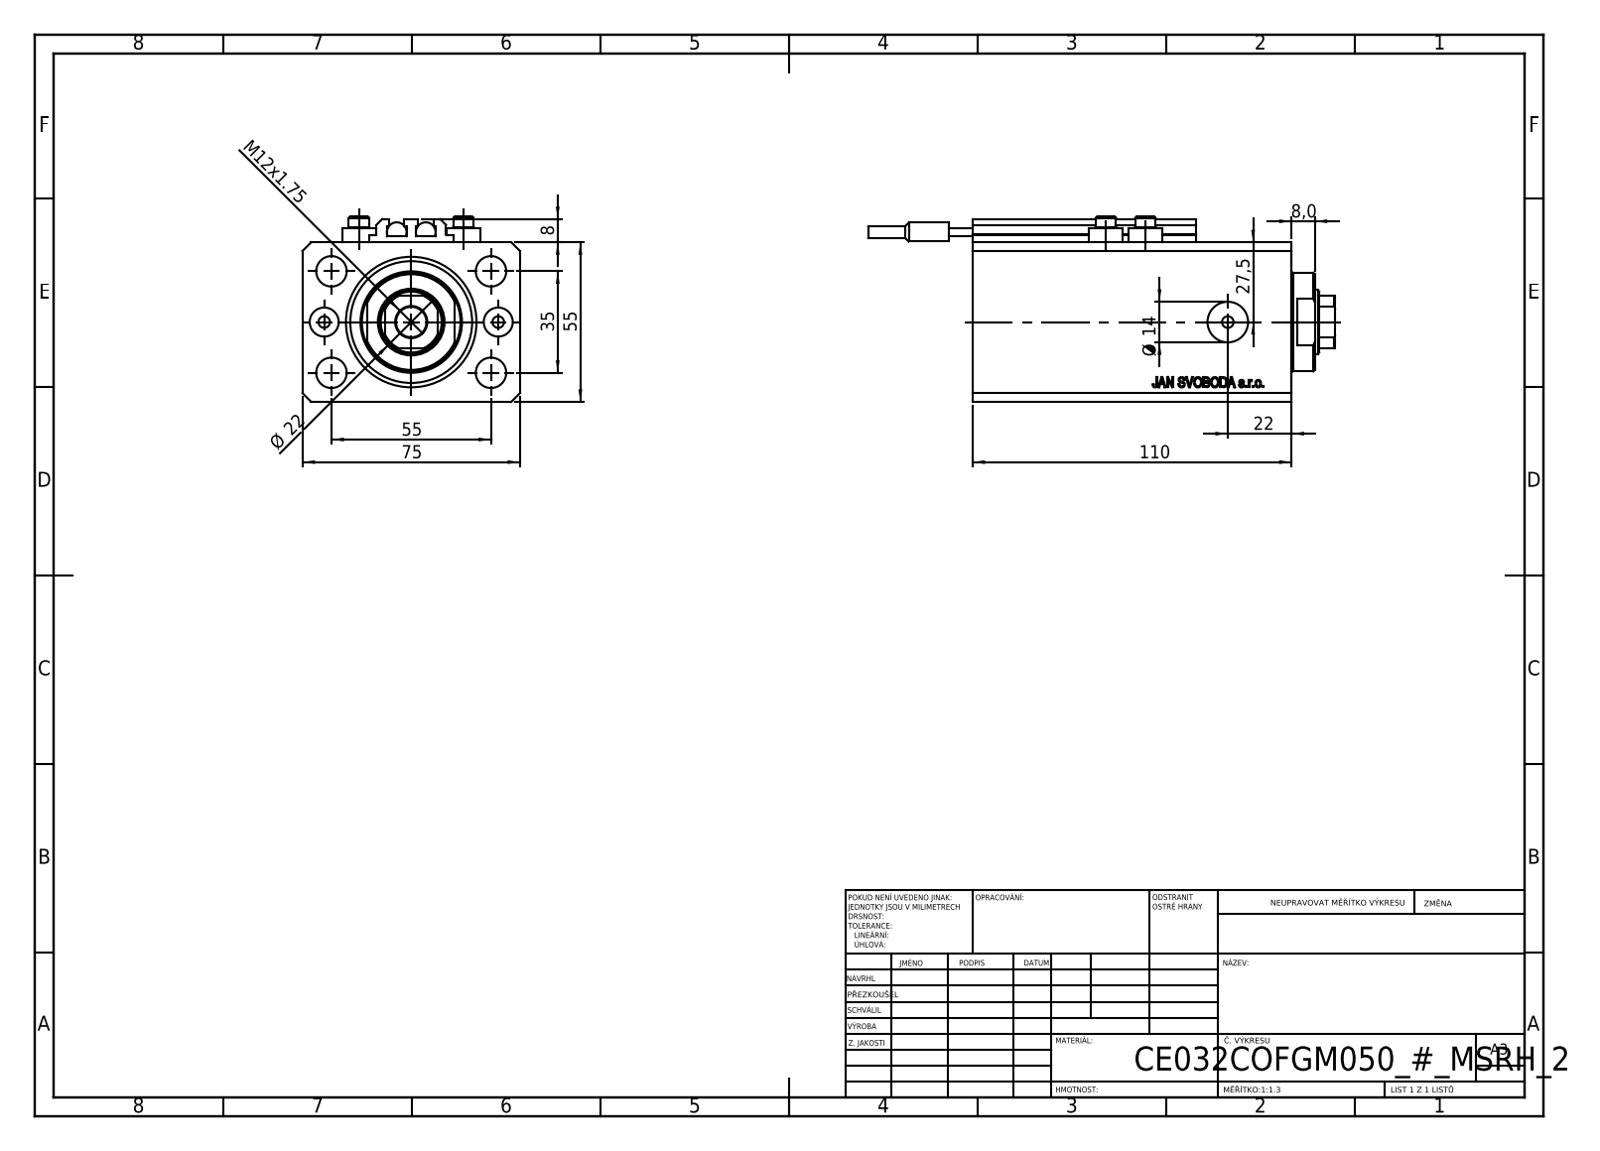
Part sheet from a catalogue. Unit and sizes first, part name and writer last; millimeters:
Units: millimetres
Overall size (bounding box): 161 × 75 × 64
Round holes (diameter × count): ⌀4 ×8, ⌀10.5 ×5, ⌀10 ×2, ⌀14 ×2, ⌀22 ×1, ⌀32 ×1, ⌀45 ×1
Round bosses / shafts (diameter × count): ⌀11.6 ×4, ⌀7 ×4, ⌀6.8 ×2, ⌀6.5 ×2, ⌀4 ×2, ⌀34 ×1
Partial cylindrical surfaces — rounded edges, fillets, slot ends (radius × count): R0.2 ×10, R10.5 ×1
Main face-to-face distances: 55, 75, 110, 15, 95, 3, 9.9, 85.1, 100.1, 2
Hole centre spacings: 17.68, 32.6, 60.1, 13.6, 30, 35, 36, 38.48
Volume: 412 504 mm³ · Surface area: 93 867 mm²
Bodies: 10 solids, 1086 faces (536 planar, 98 cylindrical, 452 other)
Part name (STEP PRODUCT): V250CE_VC_C; V250CE_C_Body; ALLEN BOLT V250CE; SWITCH_V250CE (+1 more)
STEP written by: SolidWorks 2019 (CONFIG_CONTROL_DESIGN)
